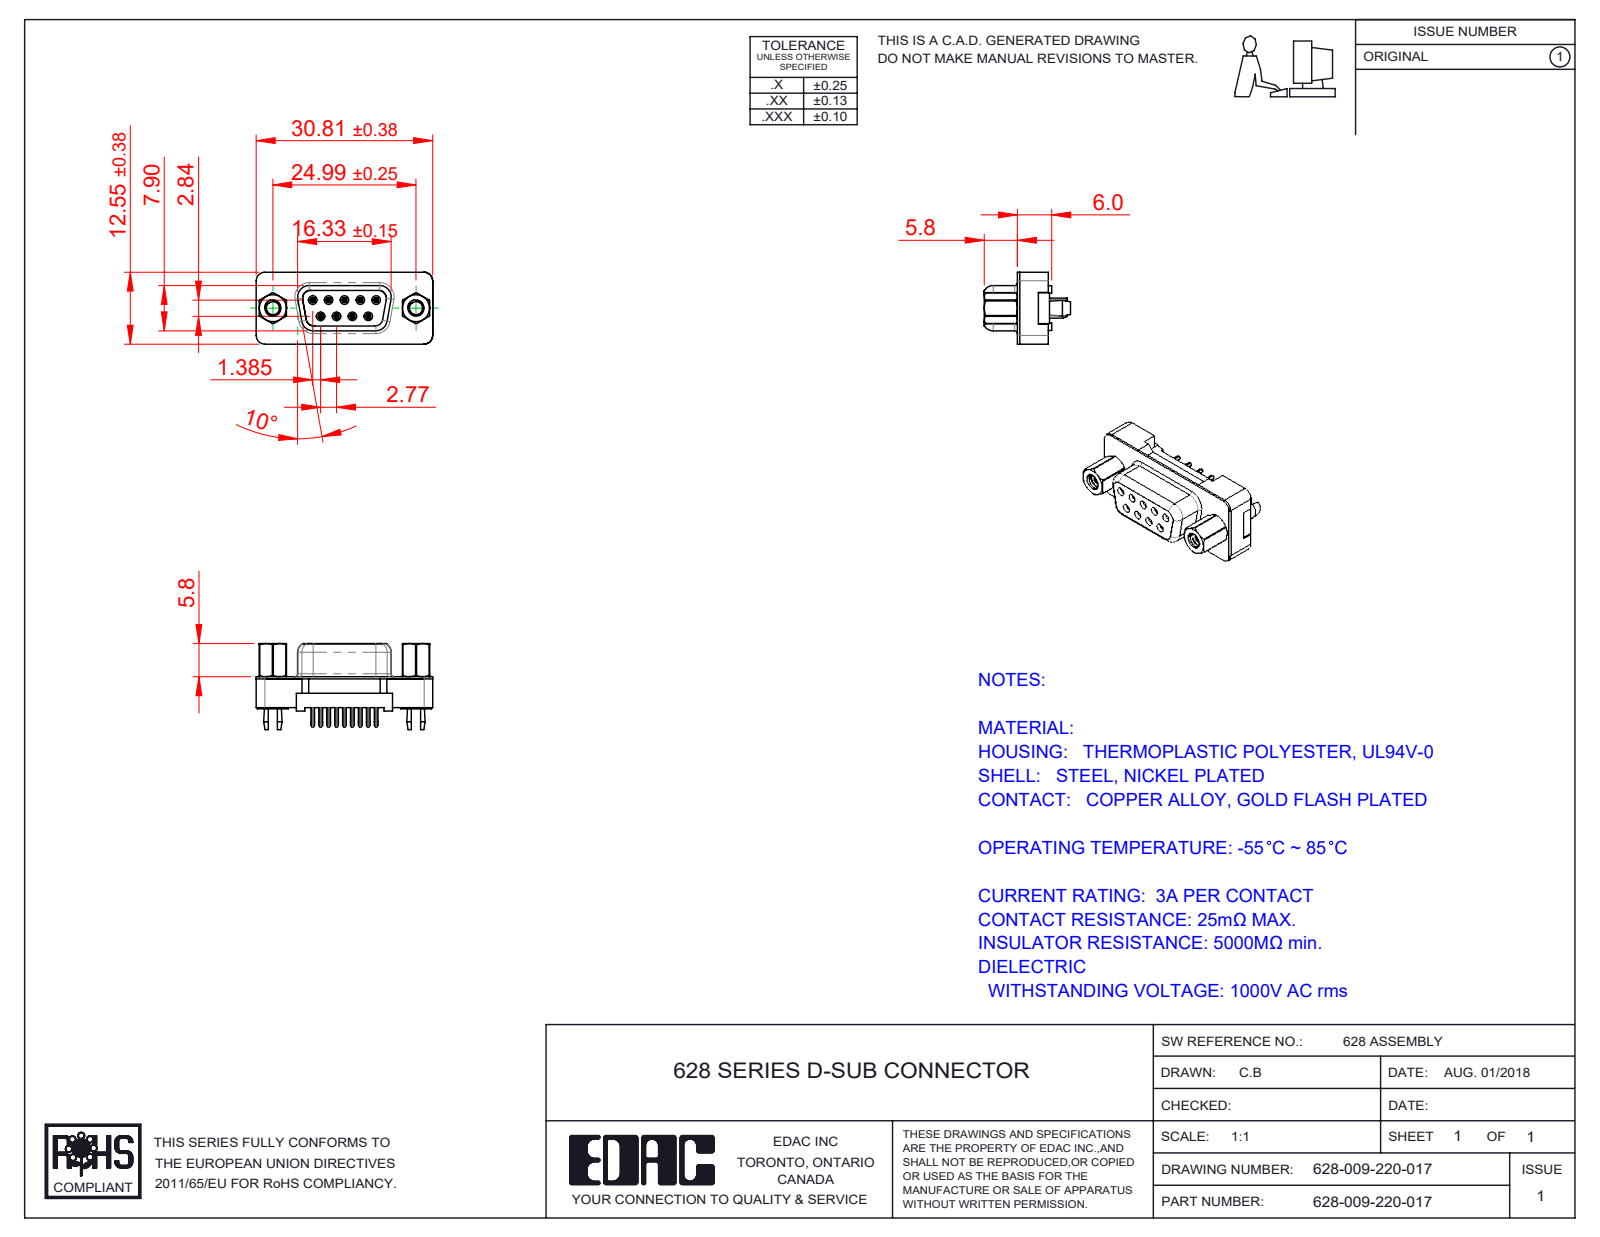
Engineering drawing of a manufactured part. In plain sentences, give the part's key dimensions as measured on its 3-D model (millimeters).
The part is named "628 Plastic Body Housing_09 Contacts; 628 PB Shell_09 Contacts; 628 4-40 Hex Standoff; 628 PB 4-40 Threaded Rivet with Boardlock (+3 more)". Its 3-D file was written by "SolidWorks 2020 (CONFIG_CONTROL_DESIGN)". It is 15 solids with 1053 faces: 410 planar, 314 cylindrical and 329 other. Overall it measures 30.82 by 15.05 by 12.55 millimeters. Its volume is 2 204 cubic millimeters and its surface area 4 942 square millimeters. Round holes: 9 of diameter 0.9, 2 of diameter 2.26, 2 of diameter 2.29, 2 of diameter 3.05, 2 of diameter 4, 2 of diameter 4.8, 2 of diameter 5. Round bosses or shafts: 2 of diameter 4.9, 2 of diameter 2.79. Partial cylindrical surfaces (rounded edges, fillets, slot ends): 36 of radius 0.25, 13 of radius 0.5, 11 of radius 1.35, 9 of radius 0.3, 8 of radius 1.5, 4 of radius 0.9, 4 of radius 1.6, 4 of radius 1.75. The main face-to-face distances are 0.4, 2, 5.54, 2.77, 2.5, 6.2, 5, 5.4, 8.7, 2.7. The hole center spacings are 3.16, 2.77, 5.54, 5.03, 5.04, 8.31, 7.1, 7.48.
